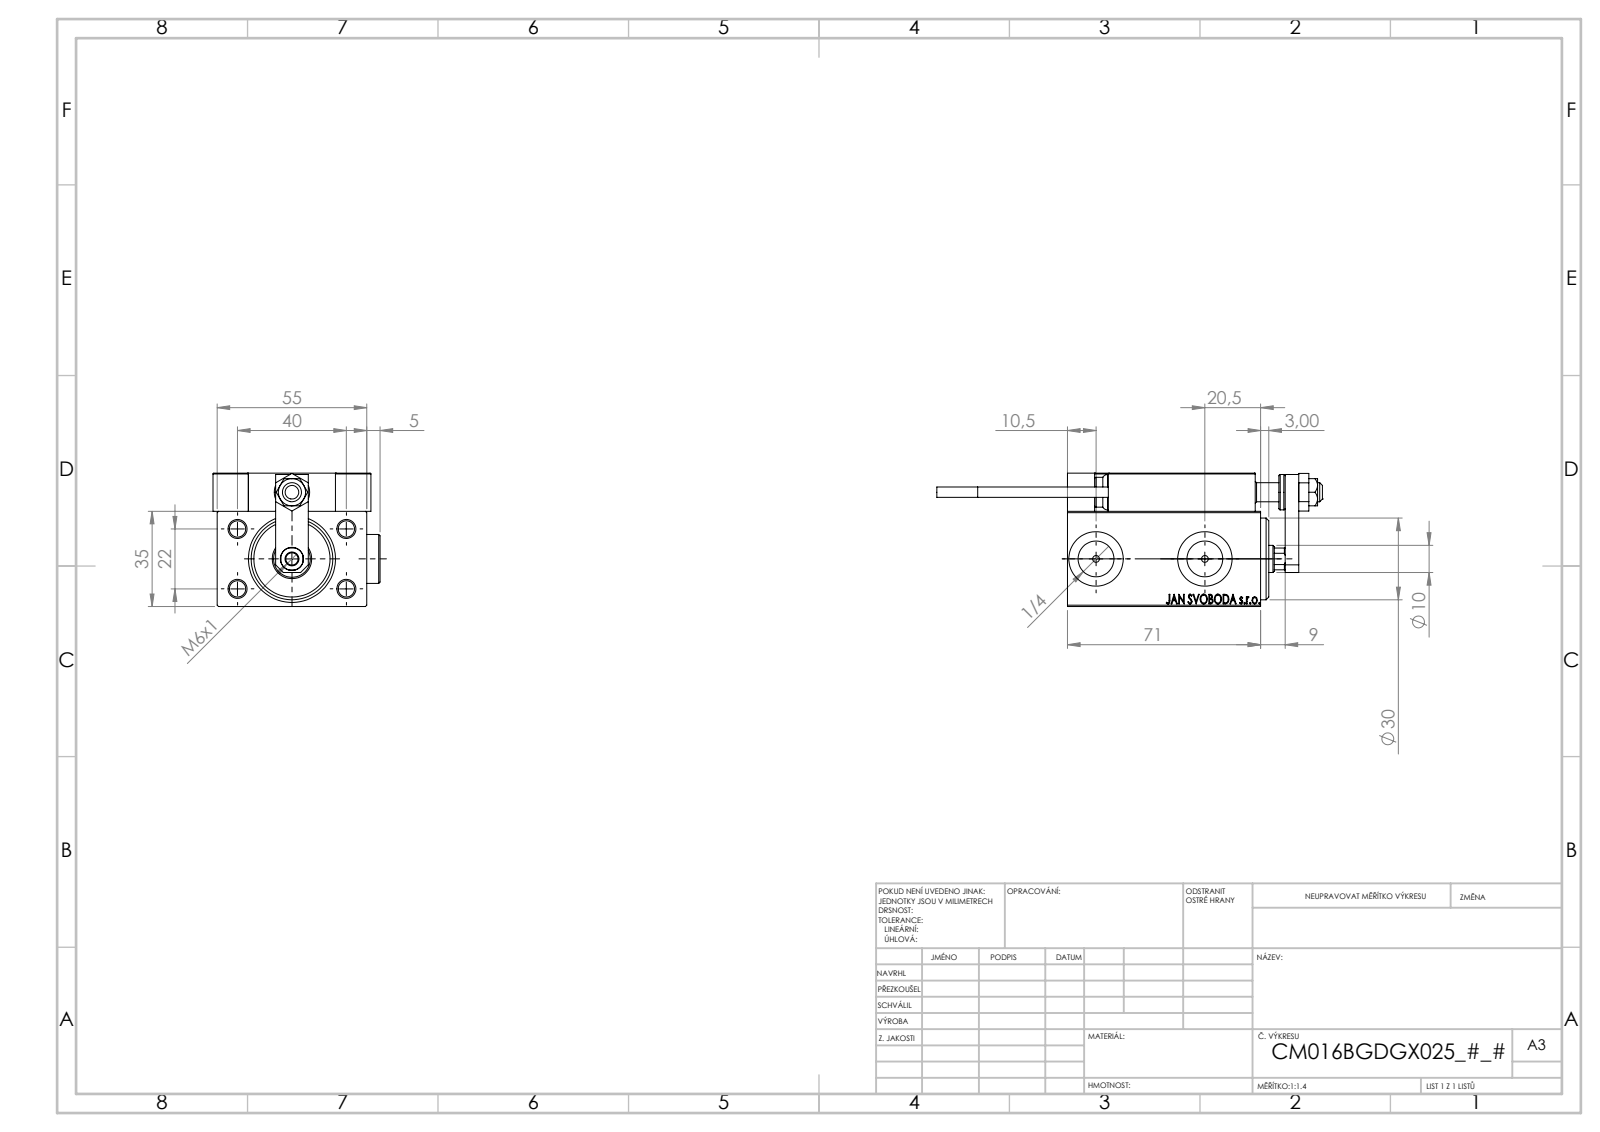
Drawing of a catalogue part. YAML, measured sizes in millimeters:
part_name: "ALLEN BOLT D5; ALLEN BOLT D8; V450CM_VC_B; V450CM_B_Body (+7 more)"
step_written_by: "SolidWorks 2019 (CONFIG_CONTROL_DESIGN)"
units: millimeters
bodies: {solids: 26, faces: 1372, planar: 595, cylindrical: 200, other: 577}
overall_size: [141.7, 61.4, 49]
volume: 170569
surface_area: 53744
round_holes:
  - {diameter: 8, count: 5}
  - {diameter: 3.2, count: 4}
  - {diameter: 4, count: 4}
  - {diameter: 6, count: 4}
  - {diameter: 2.5, count: 2}
  - {diameter: 5, count: 2}
  - {diameter: 13.16, count: 2}
  - {diameter: 20, count: 2}
  - {diameter: 4.5, count: 1}
  - {diameter: 7, count: 1}
  - {diameter: 8.5, count: 1}
  - {diameter: 10, count: 1}
round_bosses_or_shafts:
  - {diameter: 18, count: 2}
  - {diameter: 5, count: 2}
  - {diameter: 3.8, count: 2}
  - {diameter: 13, count: 1}
  - {diameter: 11, count: 1}
partial_cylinders:
  - {radius: 0.3, count: 30}
  - {radius: 3, count: 2}
  - {radius: 4.5, count: 1}
face_to_face_distances: [35, 5, 14, 49, 10, 3, 1.5, 55, 7, 13]
hole_center_spacings: [22.83, 40, 11.37, 20, 22, 23.09, 24.13, 29.59]
